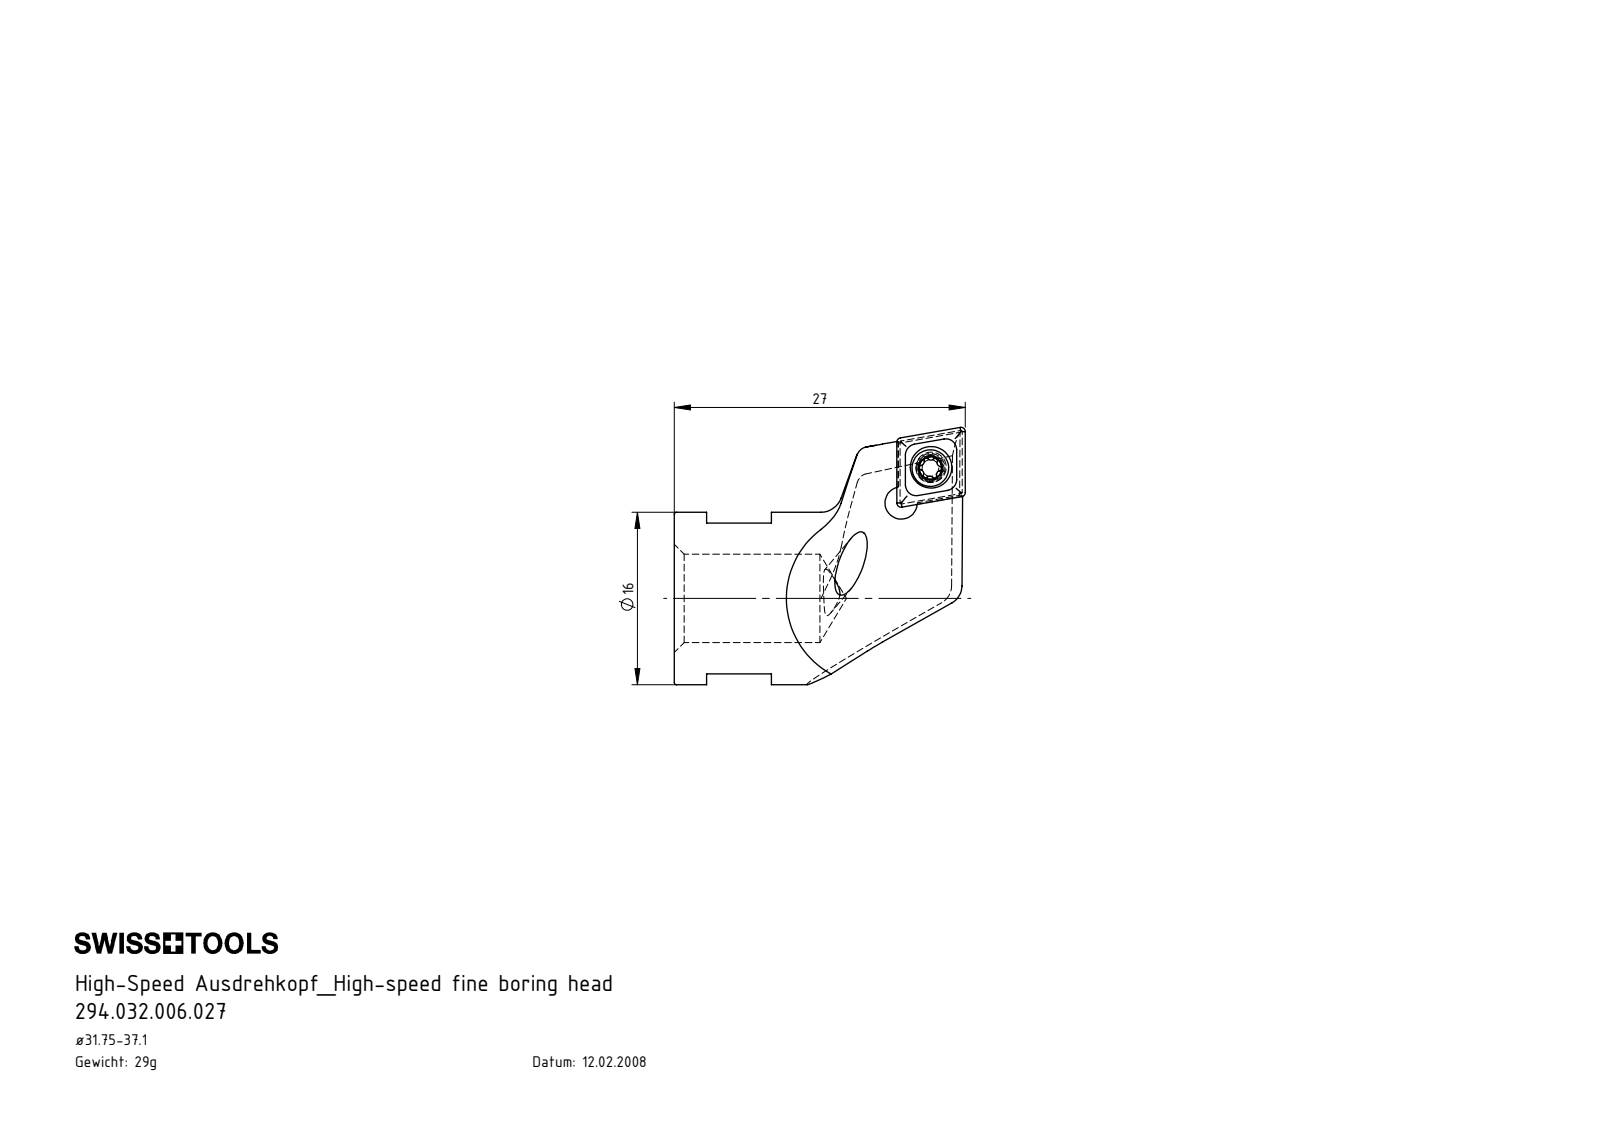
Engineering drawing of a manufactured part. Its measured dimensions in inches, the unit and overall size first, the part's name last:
Units: inches
Overall size (bounding box): 1.063 × 0.94 × 0.63
Round holes (diameter × count): ⌀0.081 ×1, ⌀0.11 ×1, ⌀0.118 ×1, ⌀0.152 ×1, ⌀0.323 ×1
Round bosses / shafts (diameter × count): ⌀0.63 ×1, ⌀0.134 ×1, ⌀0.098 ×1
Partial cylindrical surfaces — rounded edges, fillets, slot ends (radius × count): R0.008 ×6, R0.014 ×5, R0.014 ×1, R0.059 ×1, R0.071 ×1, R0.079 ×1
Main face-to-face distances: 0.311, 0.221, 0.09, 0.551, 0.236, 0.315, 0.094, 0.354, 0.118, 0.819
Volume: 0.219 in³ · Surface area: 3.585 in²
Bodies: 3 solids, 123 faces (34 planar, 35 cylindrical, 54 other)
Part name (STEP PRODUCT): WCA-ER2.001.006_A; CCMT060204; HS0-A32.K11.027_B; HS0.A32.K11.027
STEP written by: SolidWorks 2017 (AUTOMOTIVE_DESIGN)
